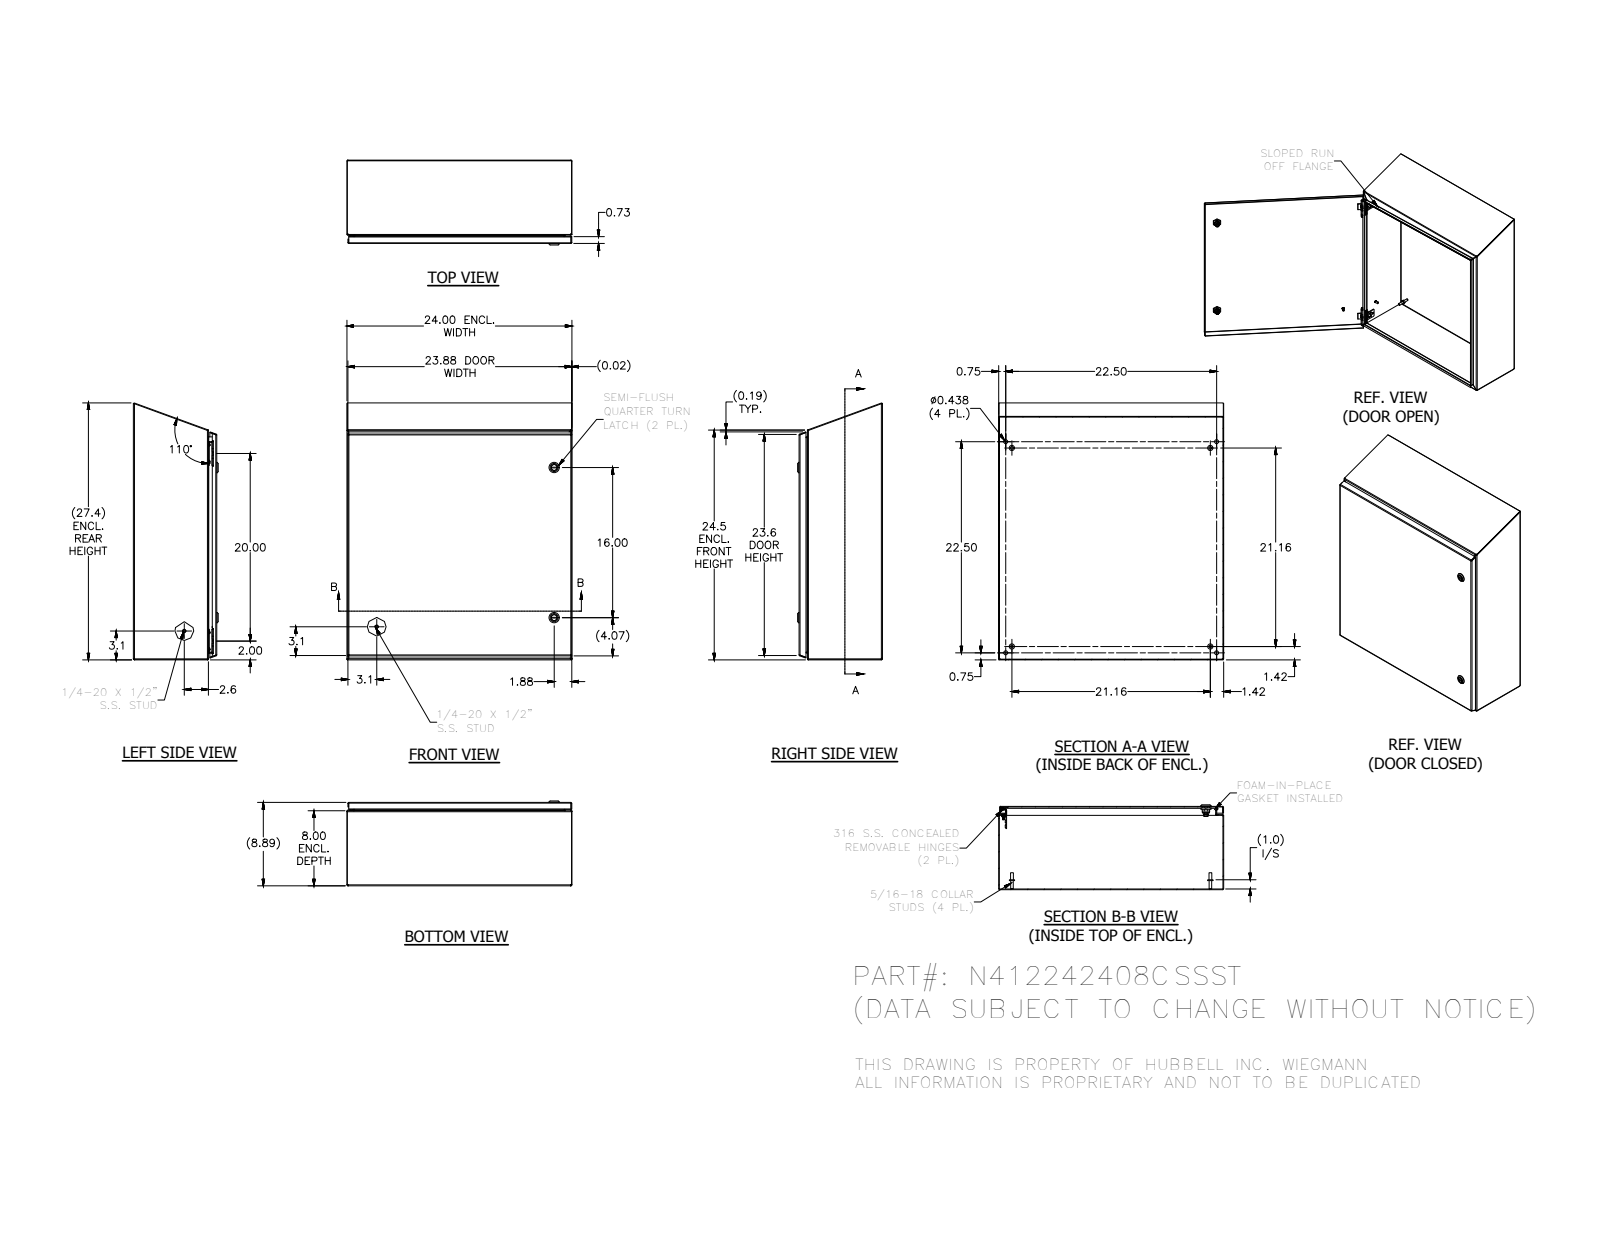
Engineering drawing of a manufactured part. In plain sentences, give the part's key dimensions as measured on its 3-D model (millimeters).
The part is named "N412242408CSSST". Its 3-D file was written by "SolidWorks 2018 (AUTOMOTIVE_DESIGN)". It is 44 solids with 1722 faces: 709 planar, 604 cylindrical and 409 other. Overall it measures 695.7 by 609.6 by 229.7 millimeters. Its volume is 2 732 000 cubic millimeters and its surface area 2 919 000 square millimeters. Round holes: 4 of diameter 2.4, 4 of diameter 3.9, 4 of diameter 4.2, 4 of diameter 4.4, 4 of diameter 4.7, 4 of diameter 11.1, 3 of diameter 4, 2 of diameter 5, 2 of diameter 8, 2 of diameter 10, 2 of diameter 10.2, 2 of diameter 16.1. Round bosses or shafts: 10 of diameter 6.4, 4 of diameter 14.3, 4 of diameter 9.1, 4 of diameter 8.1, 4 of diameter 7.6, 4 of diameter 7, 4 of diameter 6.5, 4 of diameter 4.2. Partial cylindrical surfaces (rounded edges, fillets, slot ends): 29 of radius 0.8, 26 of radius 1.3, 24 of radius 0.5, 19 of radius 2.7, 18 of radius 0.4, 16 of radius 3.2, 8 of radius 0.8, 6 of radius 4.5. The main face-to-face distances are 1.9, 223.9, 225.7, 222, 607.7, 605.8, 609.6, 201.3, 22.5, 20.7. The hole center spacings are 508, 571.5, 579.1, 12.7, 16.7, 16.8, 24.2, 33.2.
